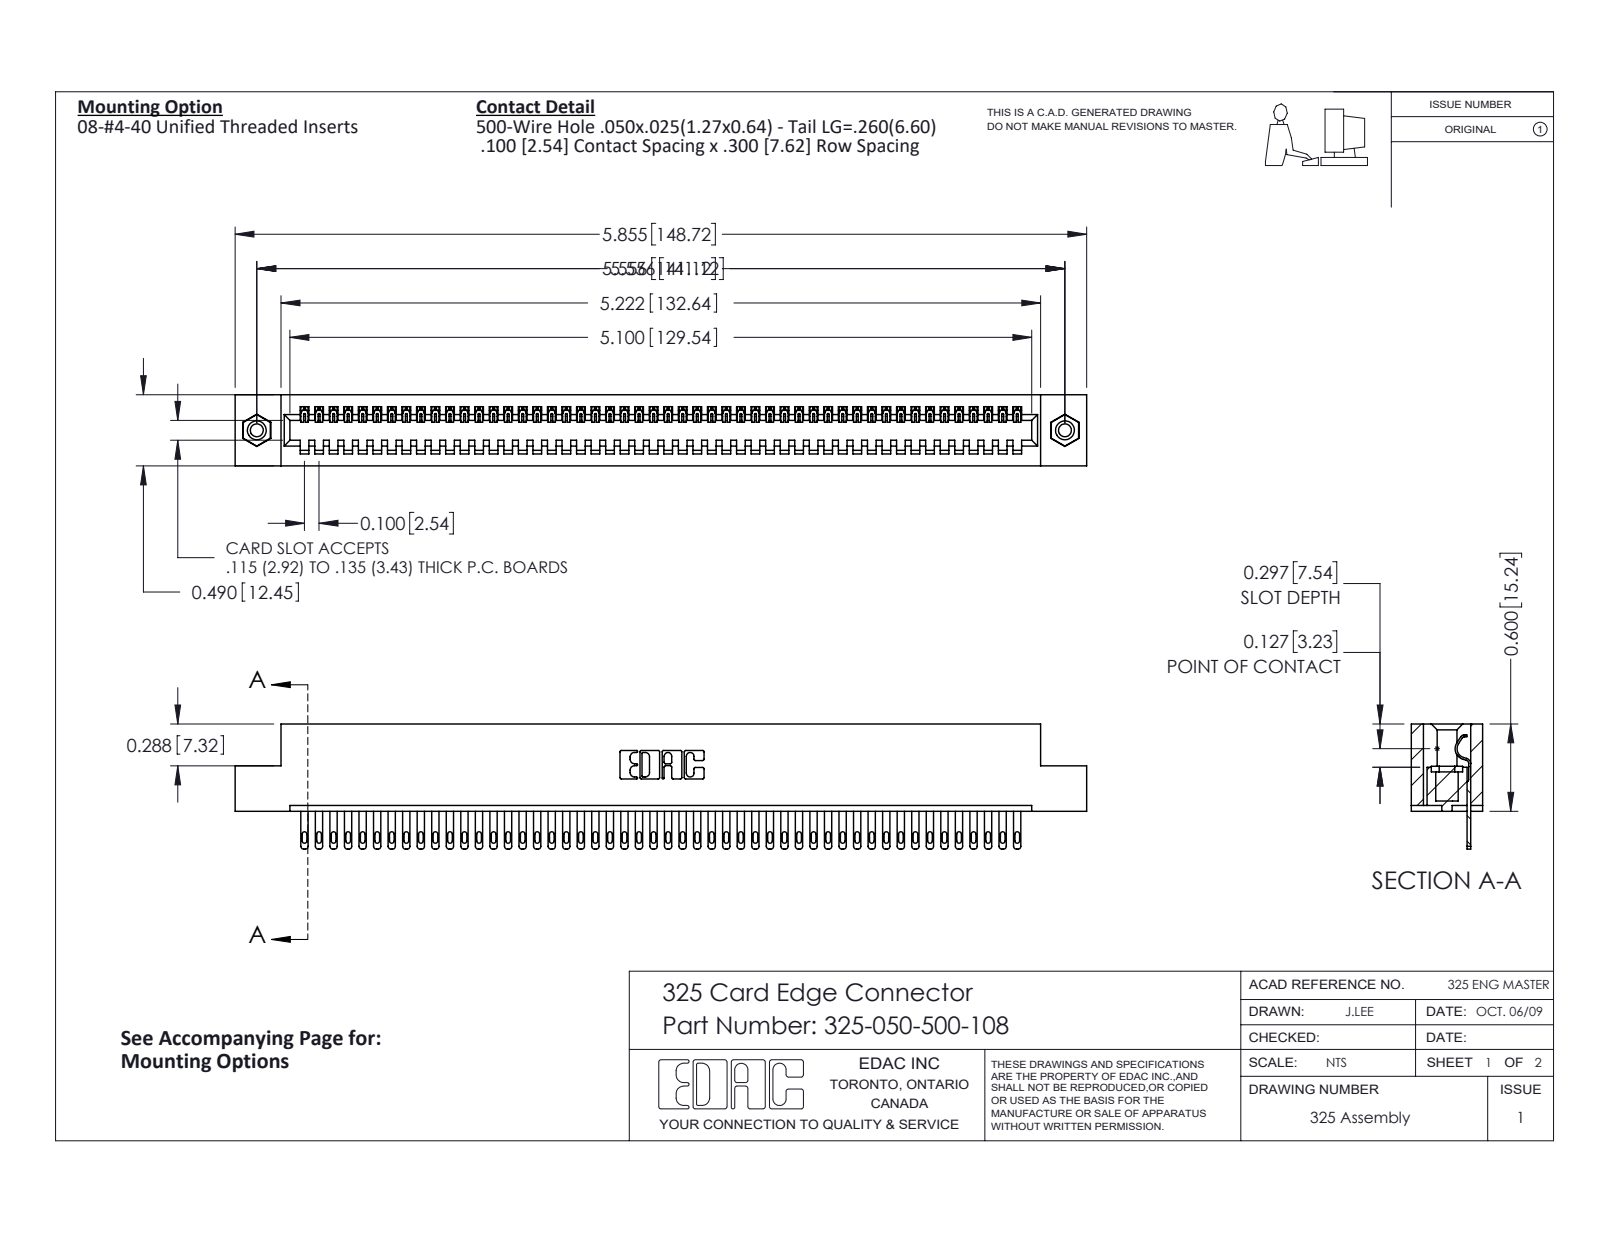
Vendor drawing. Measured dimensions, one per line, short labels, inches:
name: 345-250-001_345-250-003-102; 325-050-500-108; 325-292-001_325-293-100; 325 Part_TI
written by: SolidWorks 2016 (CONFIG_CONTROL_DESIGN)
unit: in
bodies: 53 solids, 2874 faces (1902 planar, 956 cylindrical, 16 other)
size: 5.855 × 0.86 × 0.49
volume: 1.157 in³; area: 32.53 in²
holes: 2× ⌀0.089, 2× ⌀0.125, 2× ⌀0.16
bosses: 2× ⌀0.155
rounds: 100× R0.006, 100× R0.016, 100× R0.02, 22× R0.01, 6× R0.007, 6× R0.031, 3× R0.026, 1× R0.014
face distances: 0.083, 0.407, 0.49, 0.3, 0.107, 0.383, 0.025, 0.325, 0.56, 0.263
hole spacings: 5.556
